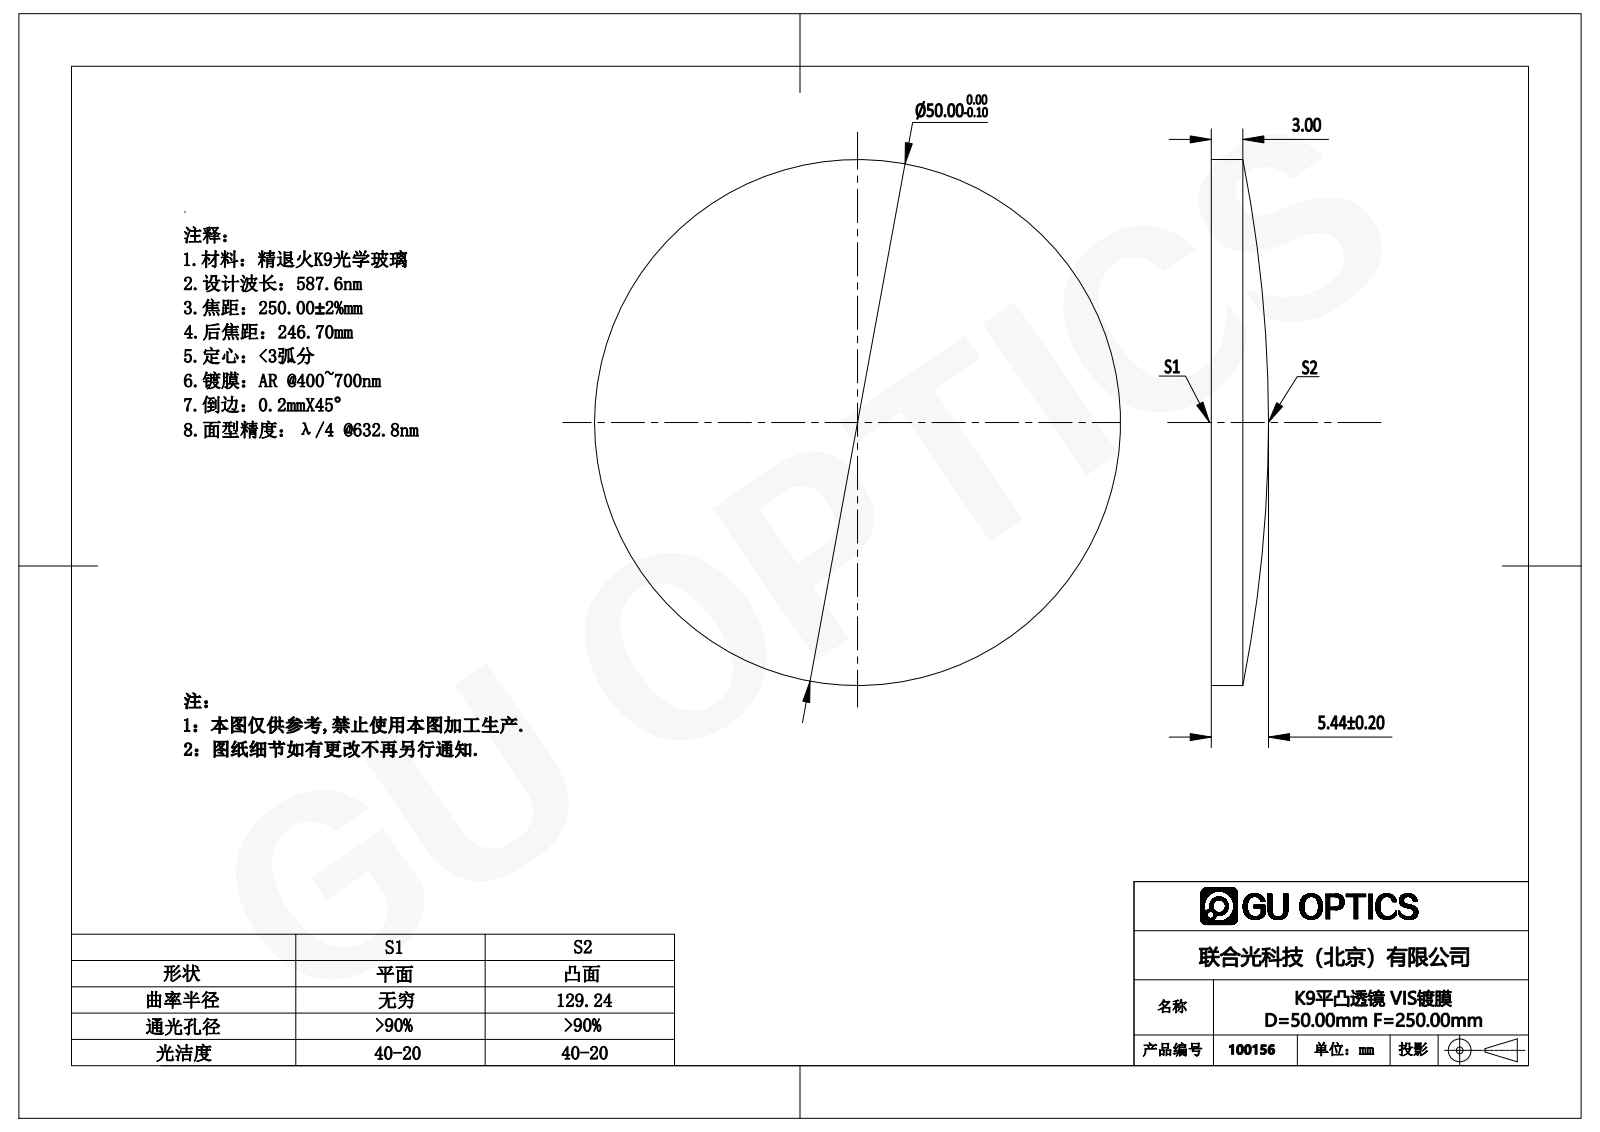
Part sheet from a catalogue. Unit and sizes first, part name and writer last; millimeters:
Units: millimetres
Overall size (bounding box): 50 × 50 × 5.44
Round bosses / shafts (diameter × count): ⌀50 ×1
Volume: 8 294 mm³ · Surface area: 4 417 mm²
Bodies: 1 solid, 5 faces (1 planar, 2 cylindrical, 2 other)
Part name (STEP PRODUCT): 100156
STEP written by: SolidWorks 2016 (AUTOMOTIVE_DESIGN)
